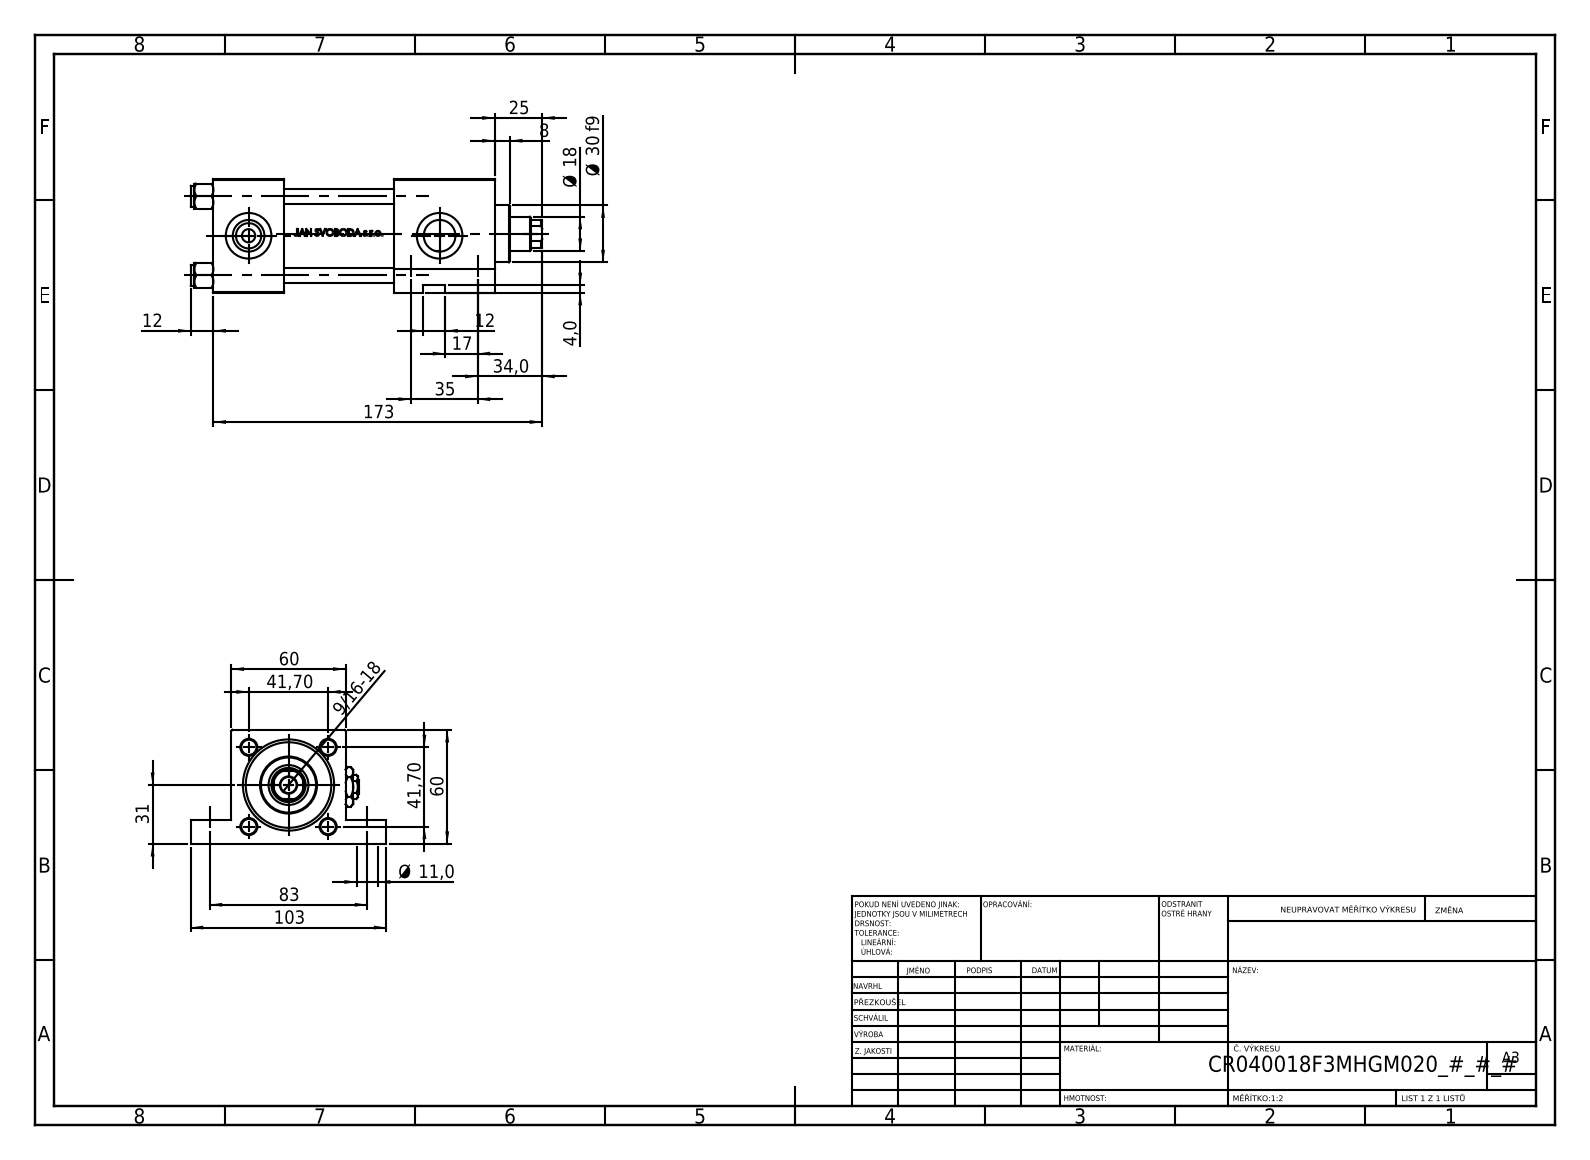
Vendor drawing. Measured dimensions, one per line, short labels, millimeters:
name: V215_VC_A; V215CR_F_Body; V215CR_VCP_F; Zatka_pro_OIL_PORT (+2 more)
written by: SolidWorks 2019 (CONFIG_CONTROL_DESIGN)
unit: mm
bodies: 13 solids, 1215 faces (484 planar, 149 cylindrical, 582 other)
size: 185 × 103 × 60
volume: 420 147 mm³; area: 114 523 mm²
holes: 4× ⌀8, 3× ⌀16.66, 3× ⌀24, 2× ⌀7, 2× ⌀11, 2× ⌀11, 1× ⌀8.5, 1× ⌀16, 1× ⌀18, 1× ⌀21, 1× ⌀31, 1× ⌀40
bosses: 4× ⌀11, 1× ⌀46, 1× ⌀30
rounds: 1× R8.5
face distances: 60, 37, 148, 111, 53, 58, 95, 119.3, 82.3, 24.3
hole spacings: 41.7, 28.79, 30.2, 35, 58.97, 83, 90.08, 8
